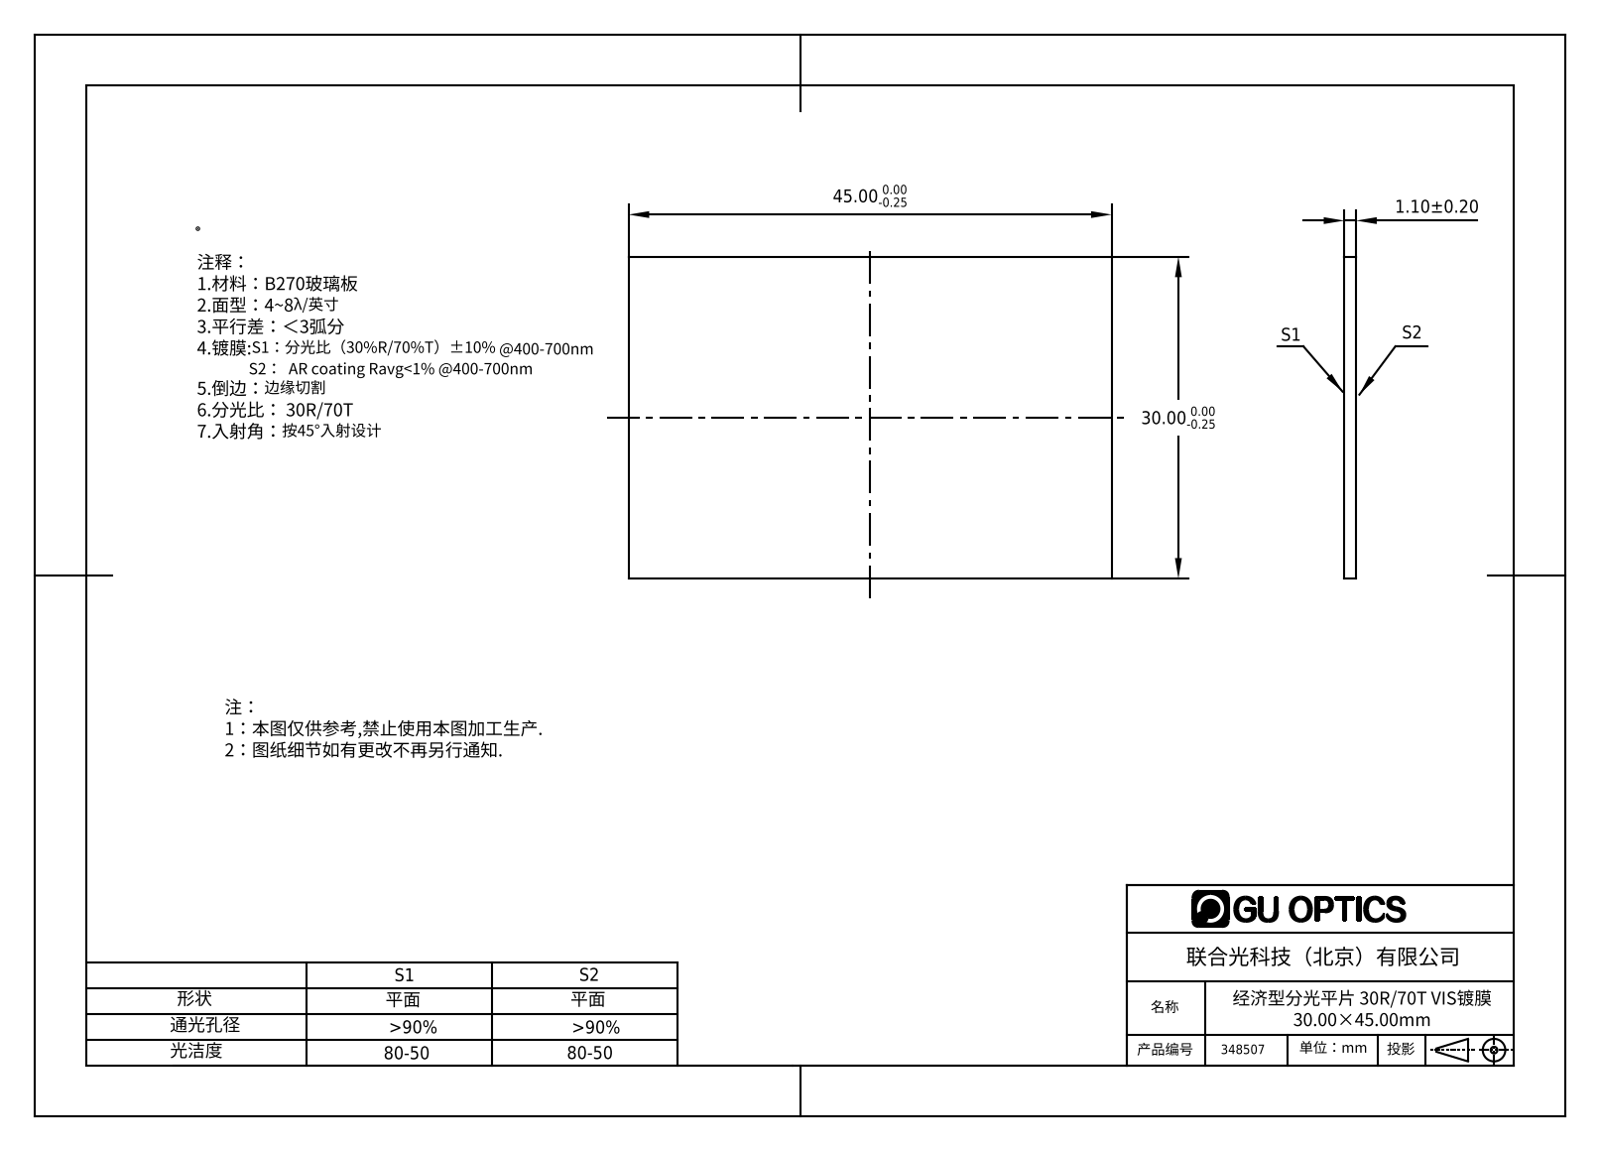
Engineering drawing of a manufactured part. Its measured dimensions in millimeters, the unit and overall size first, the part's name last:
Units: millimetres
Overall size (bounding box): 45 × 30 × 1.1
Main face-to-face distances: 1.1, 30, 45
Volume: 1 485 mm³ · Surface area: 2 865 mm²
Bodies: 1 solid, 6 faces (6 planar, 0 cylindrical, 0 other)
Part name (STEP PRODUCT): 348507
STEP written by: SolidWorks 2016 (CONFIG_CONTROL_DESIGN)
